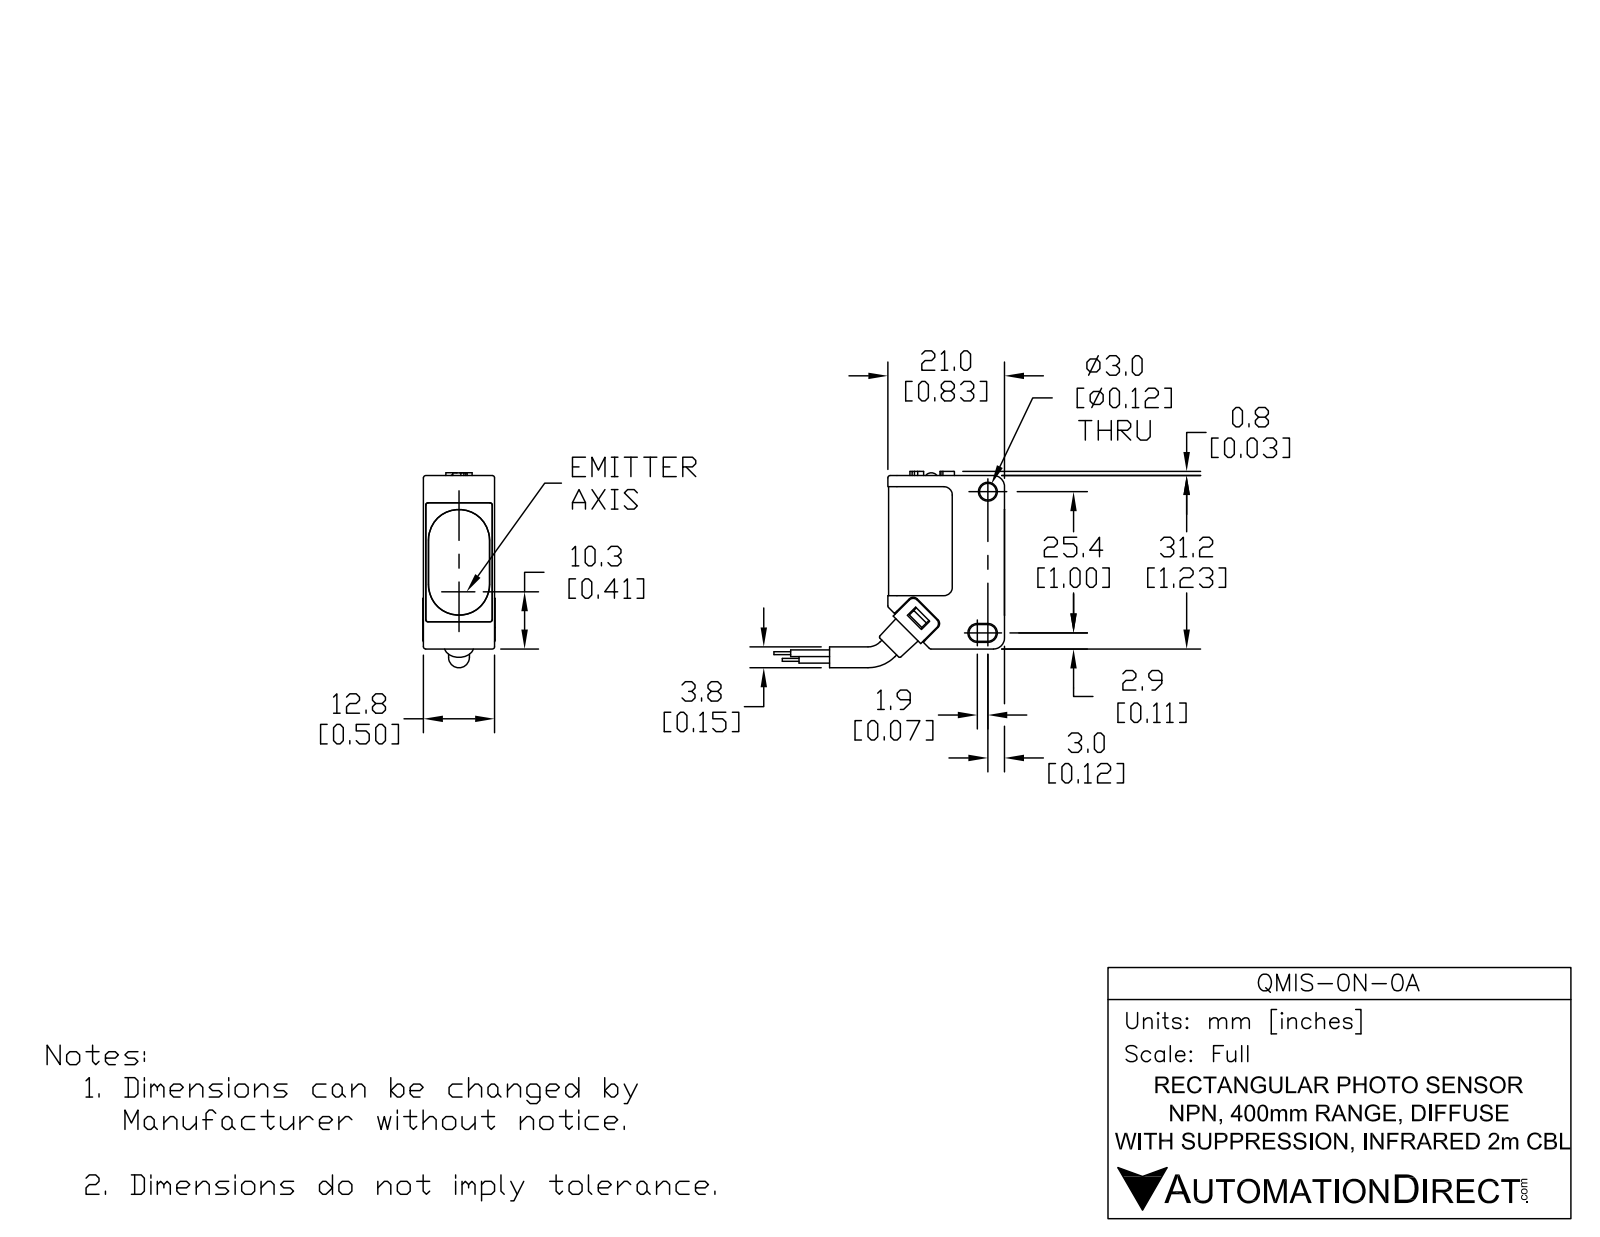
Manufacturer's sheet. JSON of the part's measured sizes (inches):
{"part_name": "QMIS-0N-0A", "step_written_by": "SolidWorks 2017 (AUTOMOTIVE_DESIGN)", "units": "inches", "bodies": {"solids": 9, "faces": 248, "planar": 132, "cylindrical": 92, "other": 24}, "overall_size": [3.193, 1.032, 0.512], "volume_in3": 0.465, "surface_area_in2": 8.347, "round_holes": [[0.118, 1], [0.148, 1], [0.173, 1], [0.224, 1], [0.283, 1]], "round_bosses_or_shafts": [[0.122, 1], [0.11, 1]], "partial_cylinders_radius": [[0.016, 13], [0.039, 8], [0.059, 7], [0.02, 4], [0.024, 4], [0.177, 4], [0.035, 2], [0.065, 2]], "face_to_face_distances": [0.498, 0.039, 0.02, 0.016, 0.504, 0.138, 0.488, 0.482, 0.098, 0.492]}
